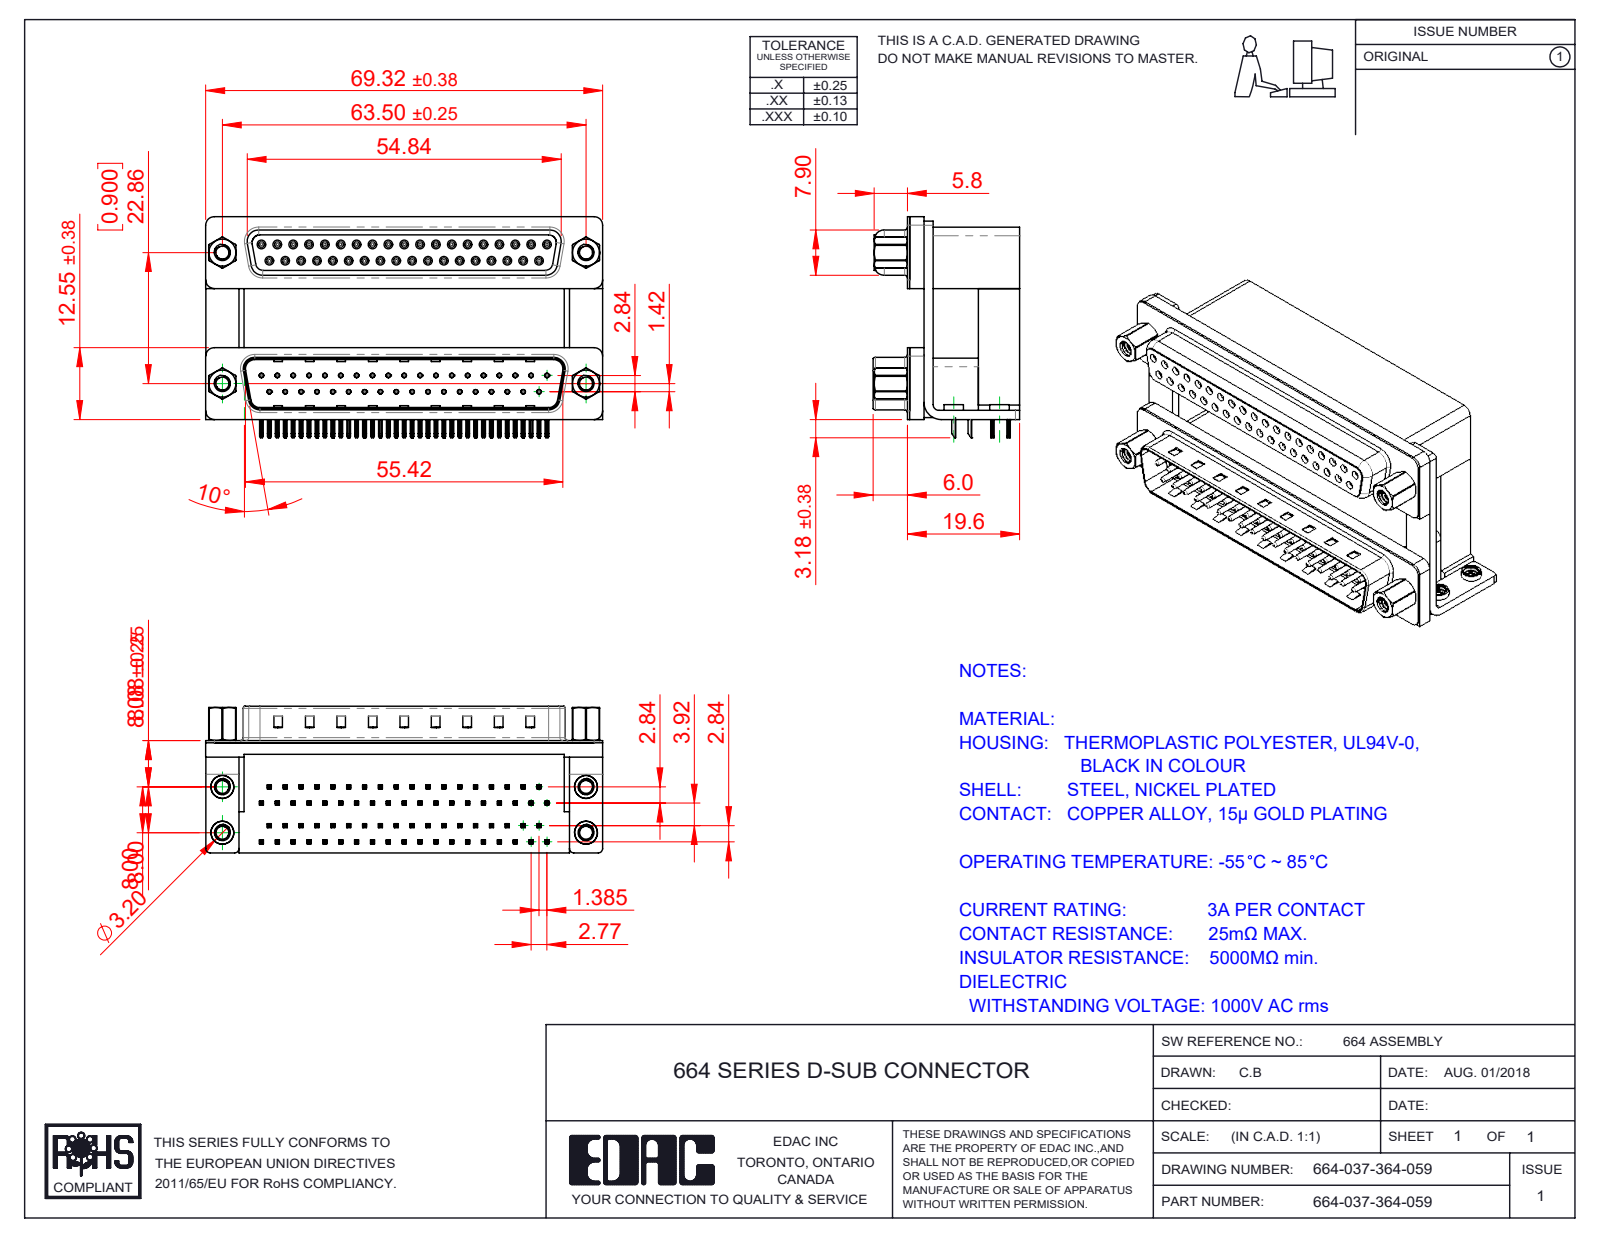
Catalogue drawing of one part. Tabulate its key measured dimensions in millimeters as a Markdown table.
| quantity | value |
| --- | --- |
| part name | 664 Housing Upper_37 Contacts H; 664 Contact Top Upper_H; 664 Housing Lower_37 Contacts; 664-037-364-059 (+8 more) |
| STEP written by | SolidWorks 2020 (CONFIG_CONTROL_DESIGN) |
| units | millimeters |
| bodies | 93 solids, 9337 faces (4797 planar, 2397 cylindrical, 2143 other) |
| overall size | 69.32 × 38.59 × 25.6 |
| volume | 33 143 mm³ |
| surface area | 35 305 mm² |
| round holes (diameter × count) | 0.8 × 74, 0.35 × 37, 0.9 × 37, 2.26 × 8, 2.29 × 4, 2.75 × 4, 3.2 × 4, 3.5 × 4, 4 × 4, 4.8 × 4, 5 × 4 |
| round bosses / shafts (diameter × count) | 1.2 × 37, 0.75 × 37, 4.9 × 4, 4.75 × 4, 4 × 4, 3.9 × 4, 3.4 × 4, 2.79 × 4 |
| partial cylindrical surfaces (radius × count) | 0.1 × 296, 0.15 × 148, 0.25 × 148, 0.12 × 74, 0.35 × 74, 0.34 × 37, 0.28 × 18, 1.5 × 13 |
| main face-to-face distances | 0.4, 19.2, 12, 7.2, 2.19, 2.84, 0.65, 22.5, 12.4, 10.69 |
| hole center spacings | 2.77, 5.54, 3.16, 8.31, 11.08, 13.85, 16.62, 19.39 |
